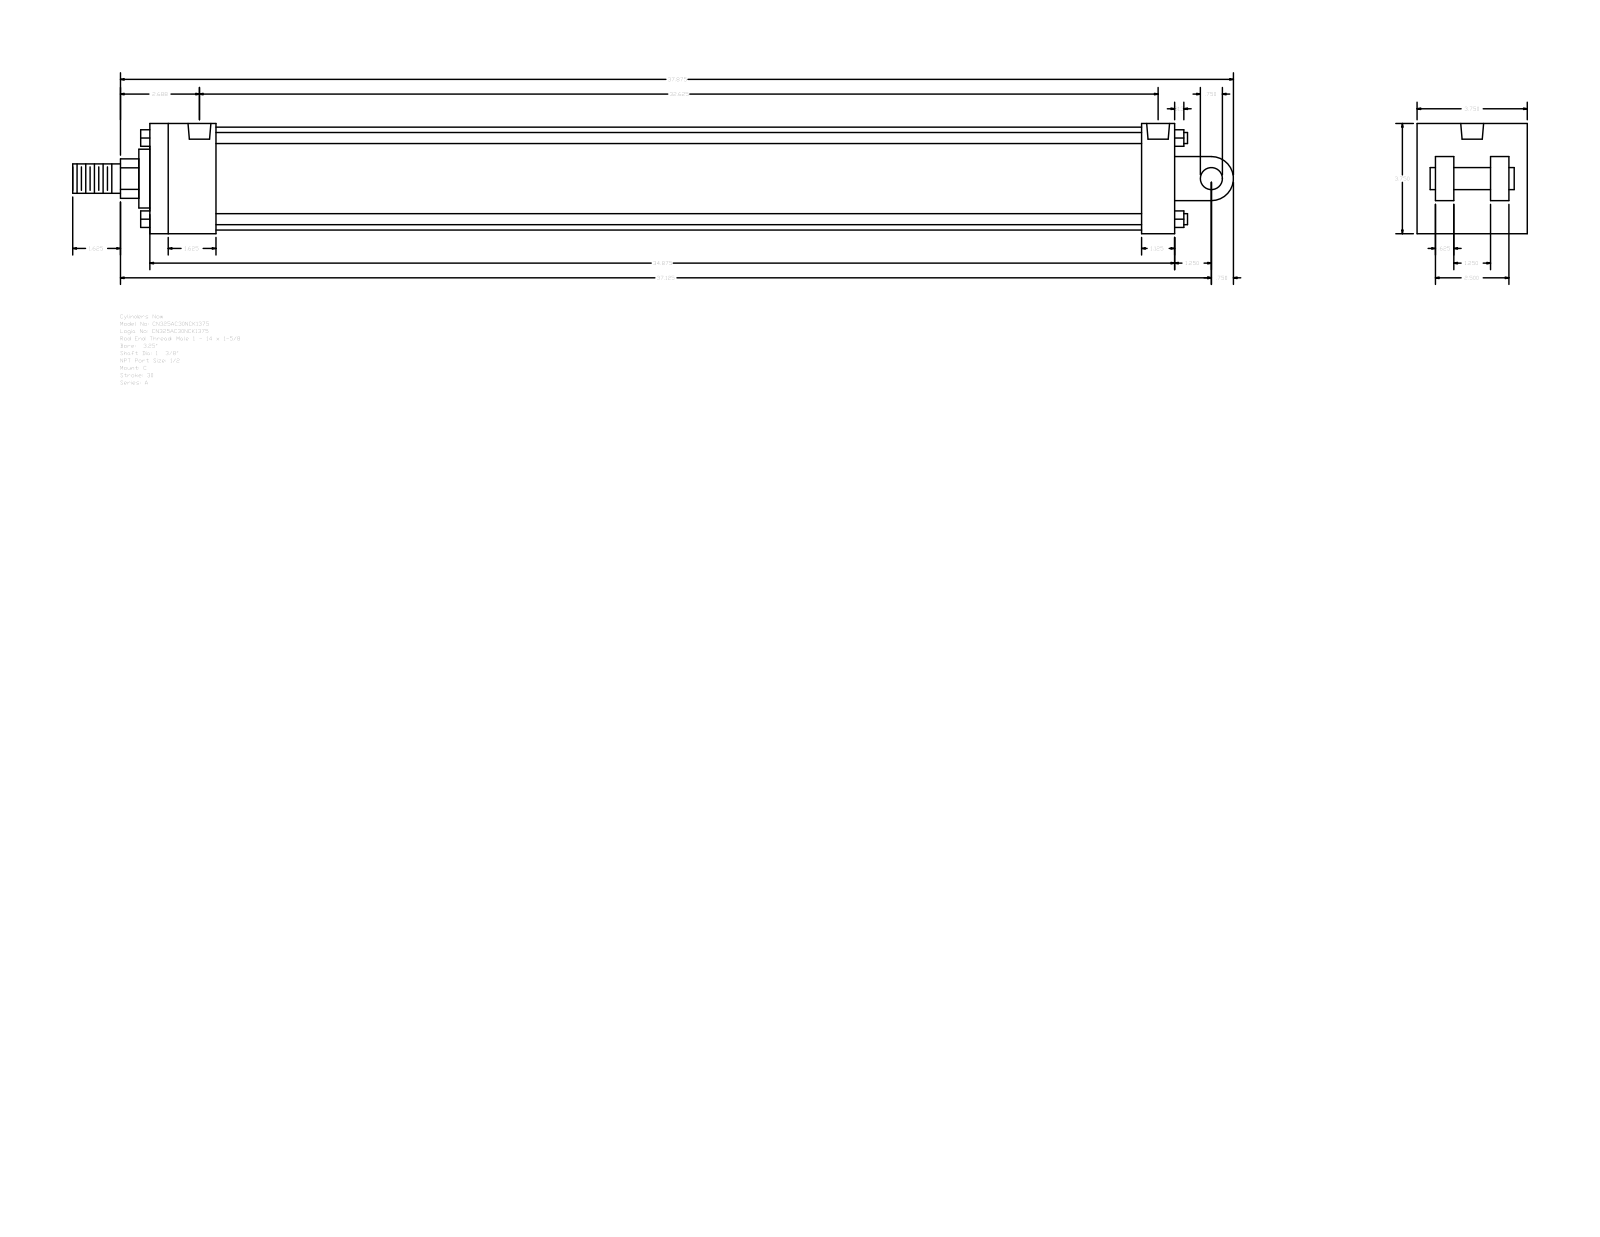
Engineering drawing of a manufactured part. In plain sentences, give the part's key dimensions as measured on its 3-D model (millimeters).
The part is named "A_C__0325_1.375". Its 3-D file was written by "GSSL Pune (CONFIG_CONTROL_DESIGN)". It is 0 solids with 135 faces: 102 planar, 33 cylindrical and 0 other. Overall it measures 1003.3 by 95.25 by 95.25 millimeters. Round holes: 4 of diameter 8.73, 2 of diameter 19.77. Round bosses or shafts: 4 of diameter 9.53, 1 of diameter 88.9, 1 of diameter 50.8, 1 of diameter 34.92, 1 of diameter 25.4, 1 of diameter 19.05. Partial cylindrical surfaces (rounded edges, fillets, slot ends): 1 of radius 17.06, 1 of radius 19.05. The main face-to-face distances are 95.24, 885.83, 15.87, 63.5, 66.67, 57.15, 28.58, 31.74, 79.37, 47.63. The hole center spacings are 3.18, 822.32, 825.5, 828.68.
